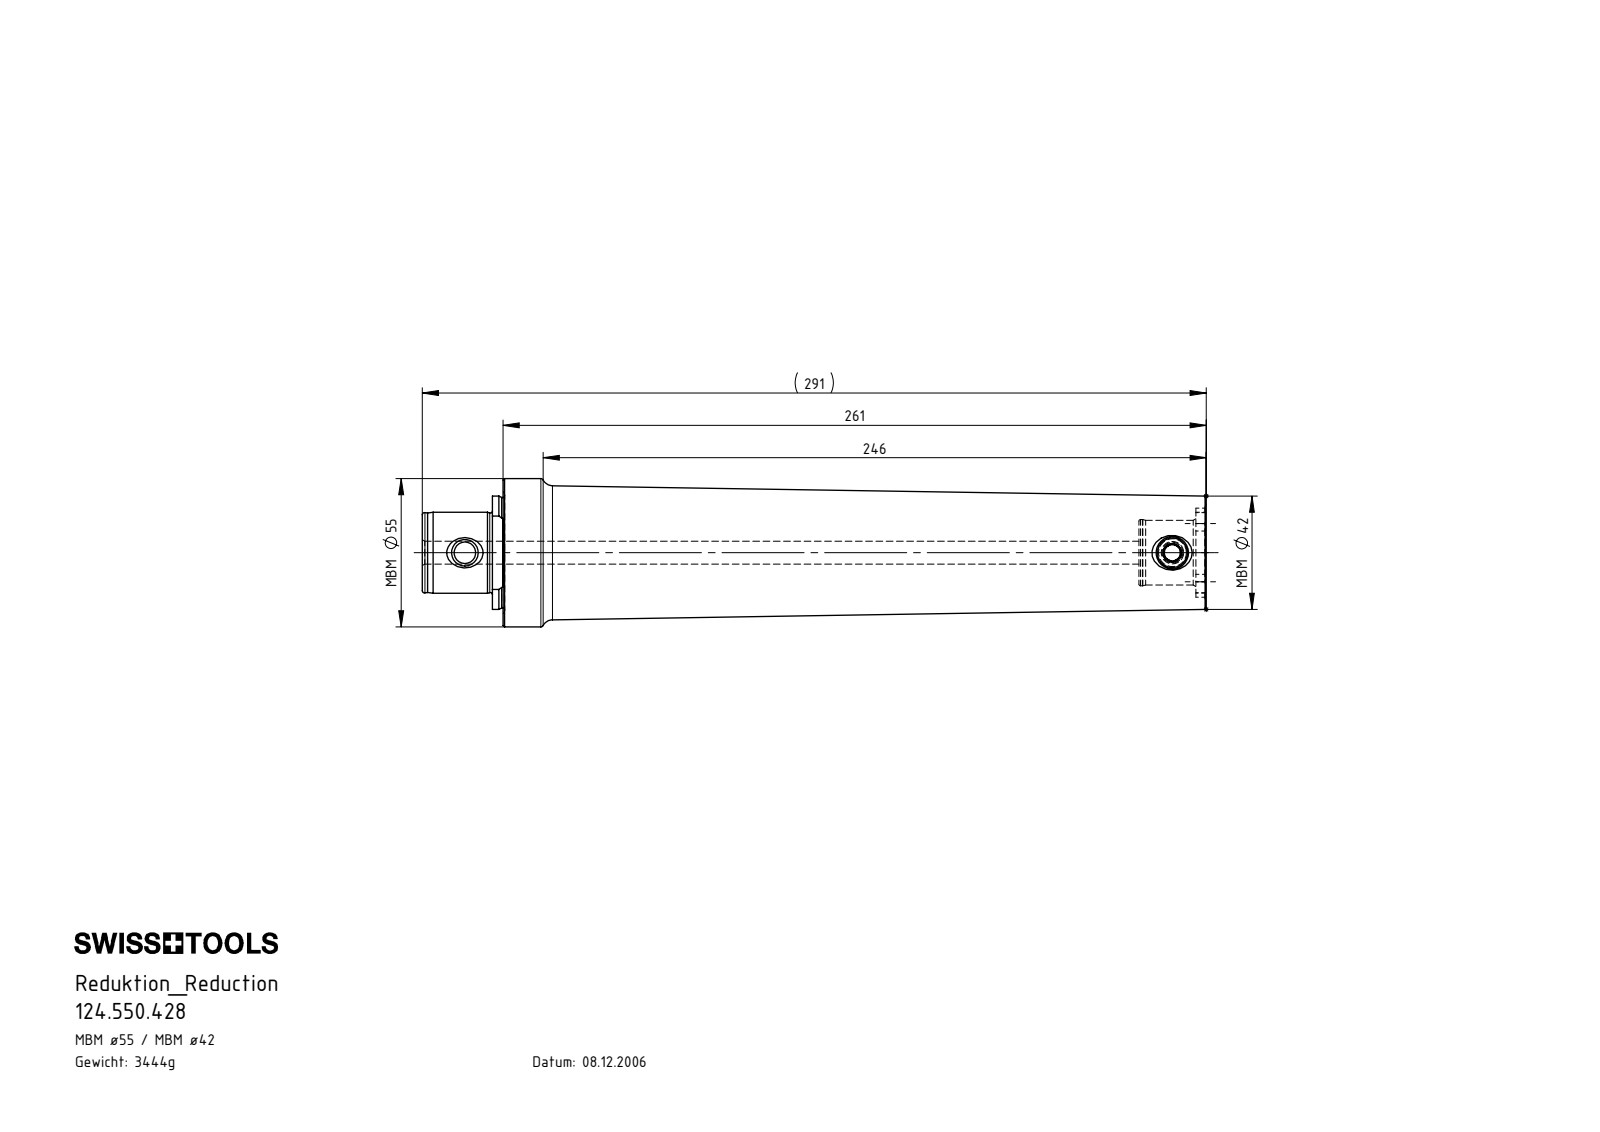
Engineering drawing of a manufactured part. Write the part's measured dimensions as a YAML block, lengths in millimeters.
part_name: "124.550.428; MB5-MB4.K01.261_C; MB4-ER1.001.013_A"
step_written_by: "SolidWorks 2017 (CONFIG_CONTROL_DESIGN)"
units: millimeters
bodies: {solids: 2, faces: 131, planar: 32, cylindrical: 32, other: 67}
overall_size: [291, 55, 55]
volume: 438761
surface_area: 54861
round_holes:
  - {diameter: 6, count: 1}
  - {diameter: 8, count: 1}
  - {diameter: 8.5, count: 1}
  - {diameter: 11, count: 1}
  - {diameter: 24, count: 1}
  - {diameter: 24.6, count: 1}
round_bosses_or_shafts:
  - {diameter: 55, count: 1}
  - {diameter: 30, count: 1}
  - {diameter: 12, count: 1}
partial_cylinders:
  - {radius: 4.2, count: 4}
  - {radius: 14.9, count: 1}
  - {radius: 16.52, count: 1}
  - {radius: 21.02, count: 1}
face_to_face_distances: [30, 26.05, 3.95, 266, 239.95, 236, 287.15, 261.1, 257.15, 21.15]
hole_center_spacings: [262.65]
